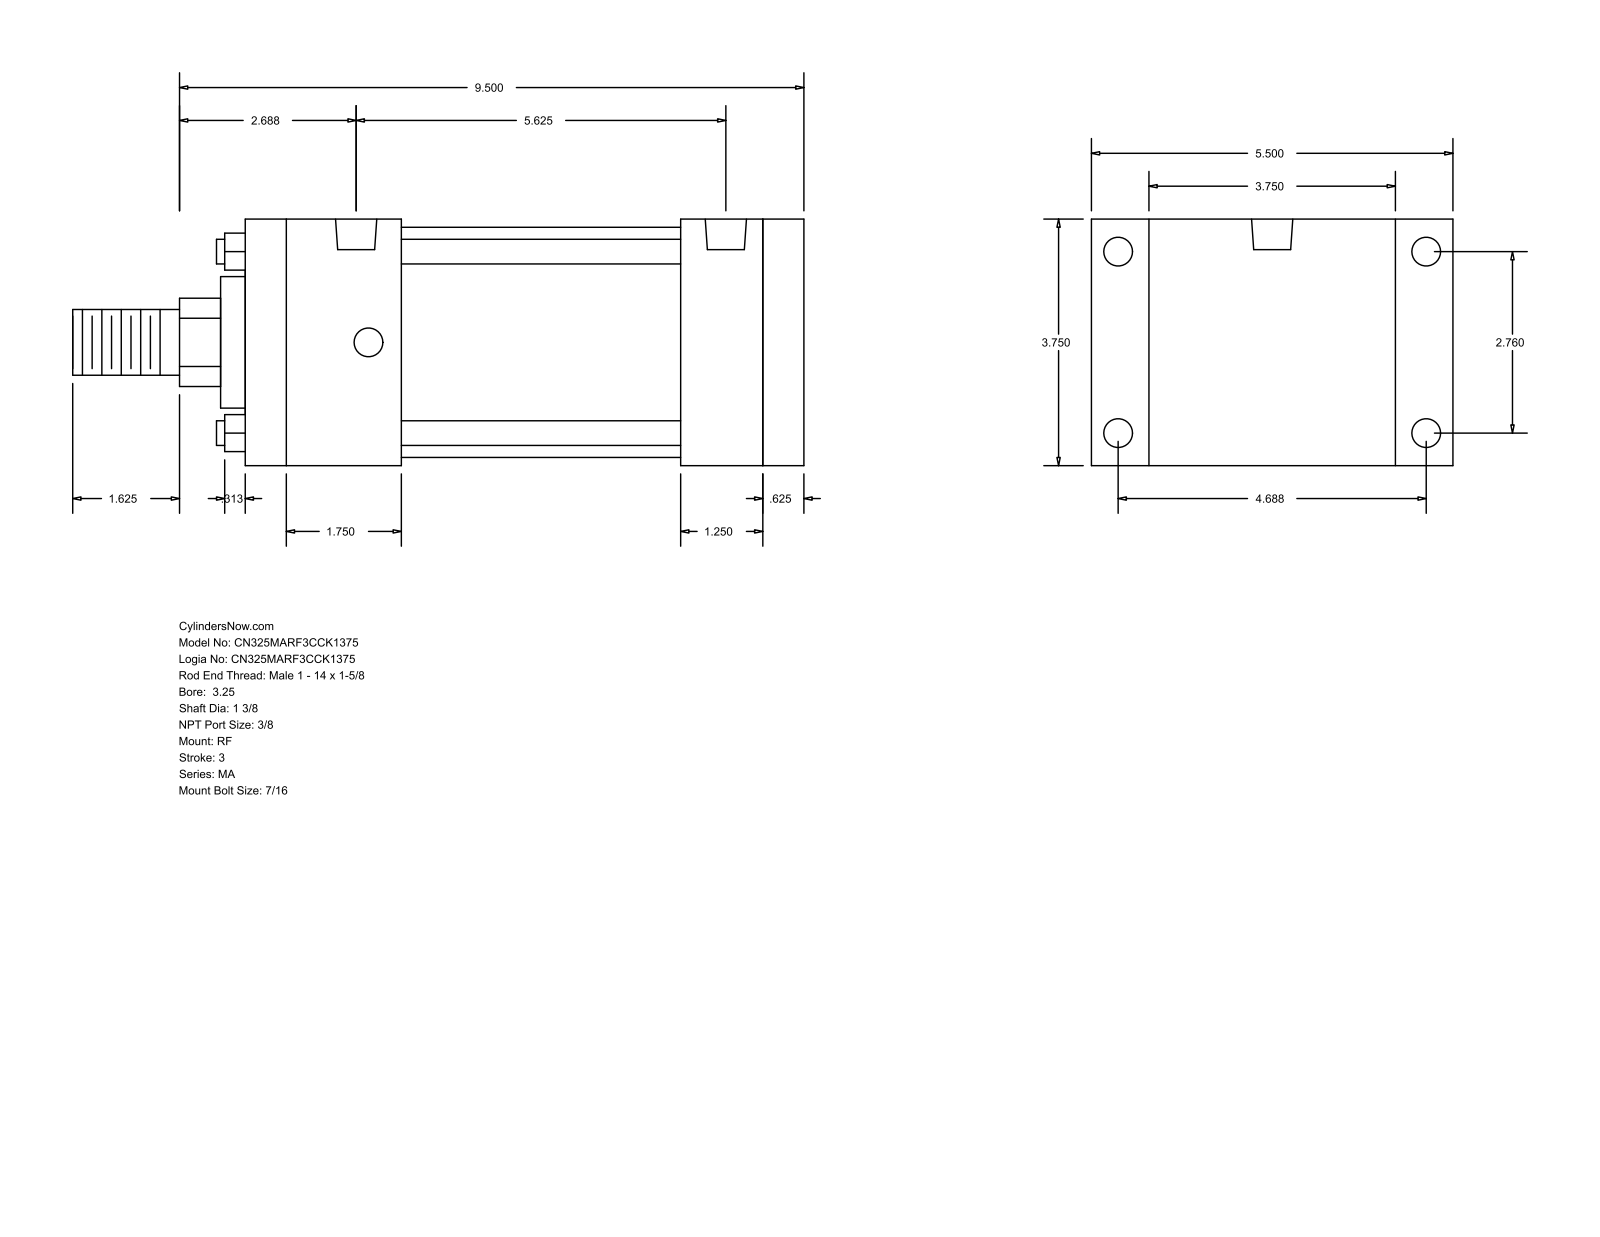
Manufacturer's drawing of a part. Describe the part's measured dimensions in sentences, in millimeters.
The part is named "MA_RF__0325_1.375". Its 3-D file was written by "GSSL Pune (CONFIG_CONTROL_DESIGN)". It is 0 solids with 92 faces: 64 planar, 28 cylindrical and 0 other. Overall it measures 282.57 by 139.7 by 95.25 millimeters. Round holes: 8 of diameter 11.11, 2 of diameter 15.93. Round bosses or shafts: 4 of diameter 9.53, 1 of diameter 88.9, 1 of diameter 50.8, 1 of diameter 34.92, 1 of diameter 25.4. Partial cylindrical surfaces (rounded edges, fillets, slot ends): 1 of radius 17.06. The main face-to-face distances are 95.24, 215.9, 200.03, 15.87, 22.23, 117.47, 168.28, 31.75, 47.62, 60.32. The hole center spacings are 70.1, 119.06, 133.35, 138.16, 4.76, 4.77, 138.11, 138.12.
